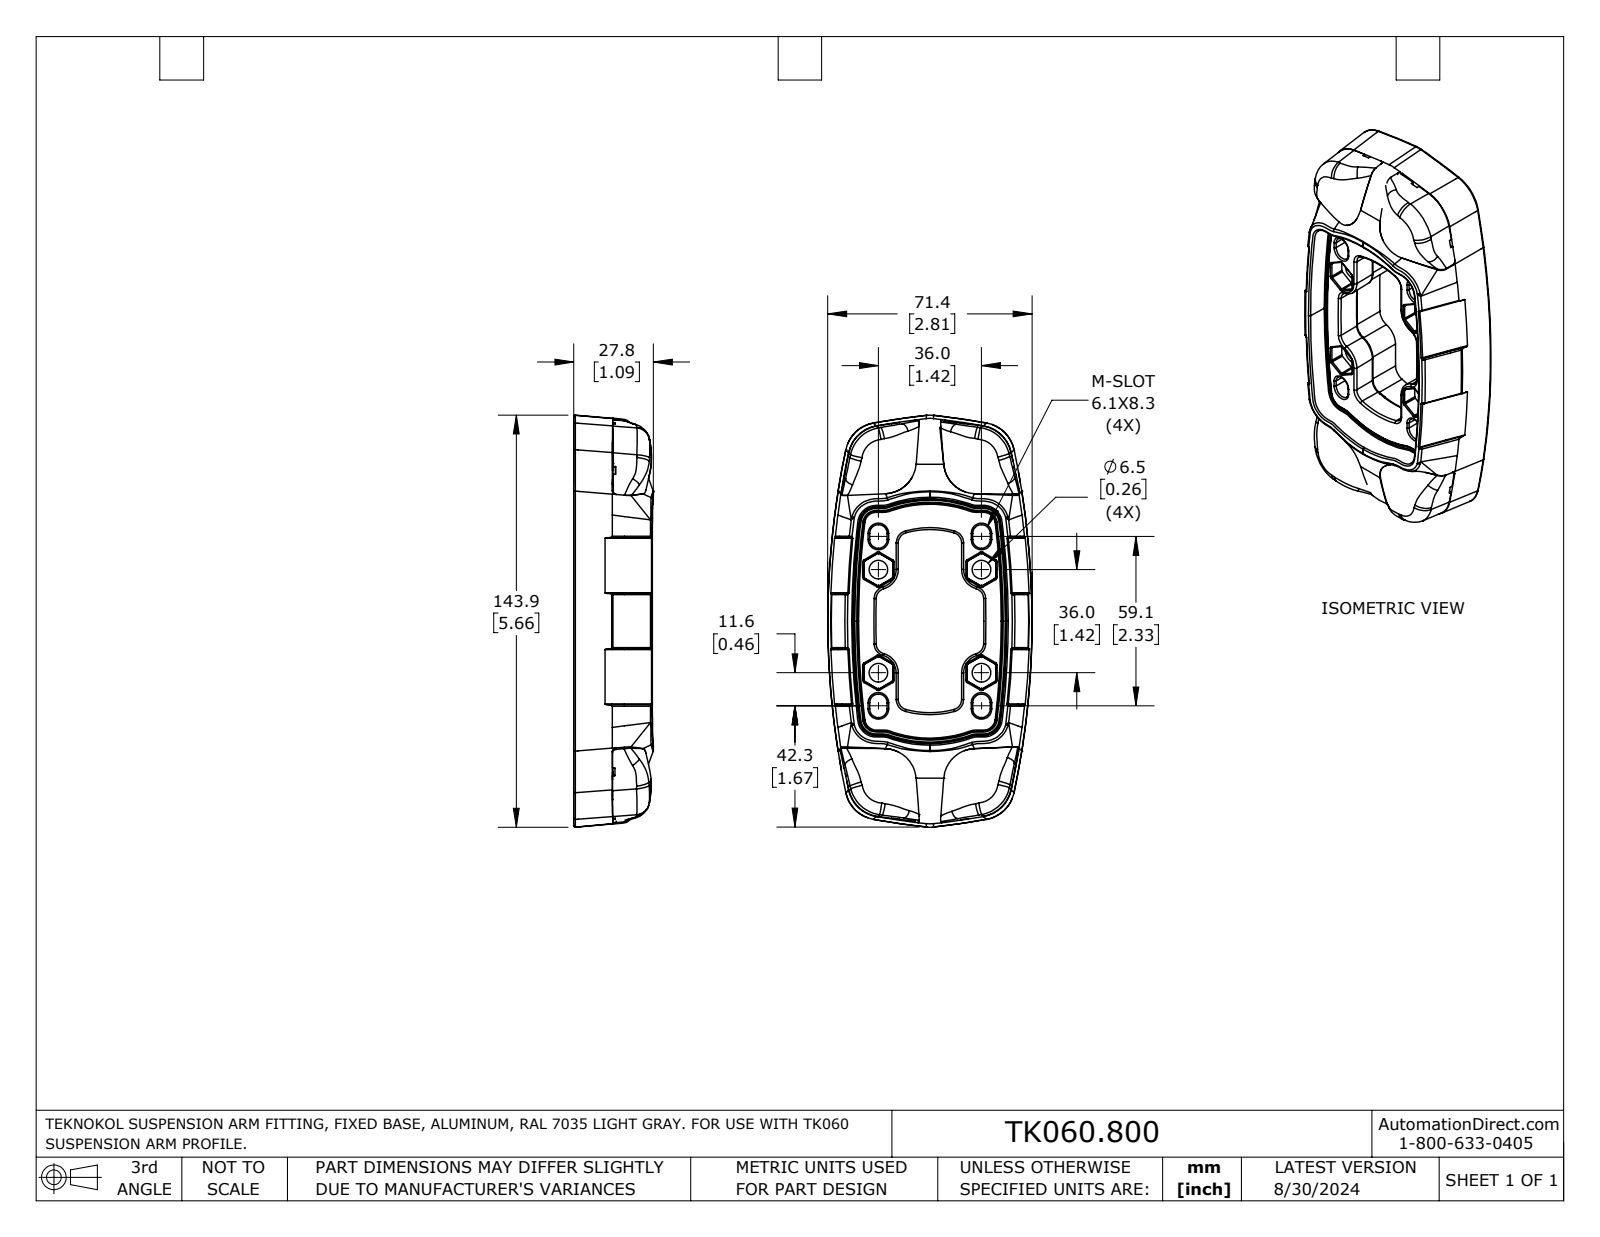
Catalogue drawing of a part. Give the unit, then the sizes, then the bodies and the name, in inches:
Units: inches
Overall size (bounding box): 5.664 × 2.81 × 1.094
Round holes (diameter × count): ⌀0.124 ×11, ⌀0.256 ×4, ⌀0.445 ×1
Round bosses / shafts (diameter × count): ⌀0.139 ×8
Partial cylindrical surfaces — rounded edges, fillets, slot ends (radius × count): R0.049 ×40, R0.02 ×24, R0.016 ×20, R0.042 ×12, R0.021 ×8, R0.052 ×8, R0.17 ×8, R0.028 ×4
Main face-to-face distances: 0.197, 0.808, 0.611, 0.306, 0.109, 0.502, 1.417, 0.602, 0.405, 0.295
Hole centre spacings: 0.907, 1.211, 1.417, 1.418, 1.846, 2.053, 2.068, 2.613
Volume: 7.553 in³ · Surface area: 75.2 in²
Bodies: 5 solids, 1022 faces (206 planar, 188 cylindrical, 628 other)
Part name (STEP PRODUCT): TK060.800
STEP written by: SolidWorks 2023 (AUTOMOTIVE_DESIGN)
